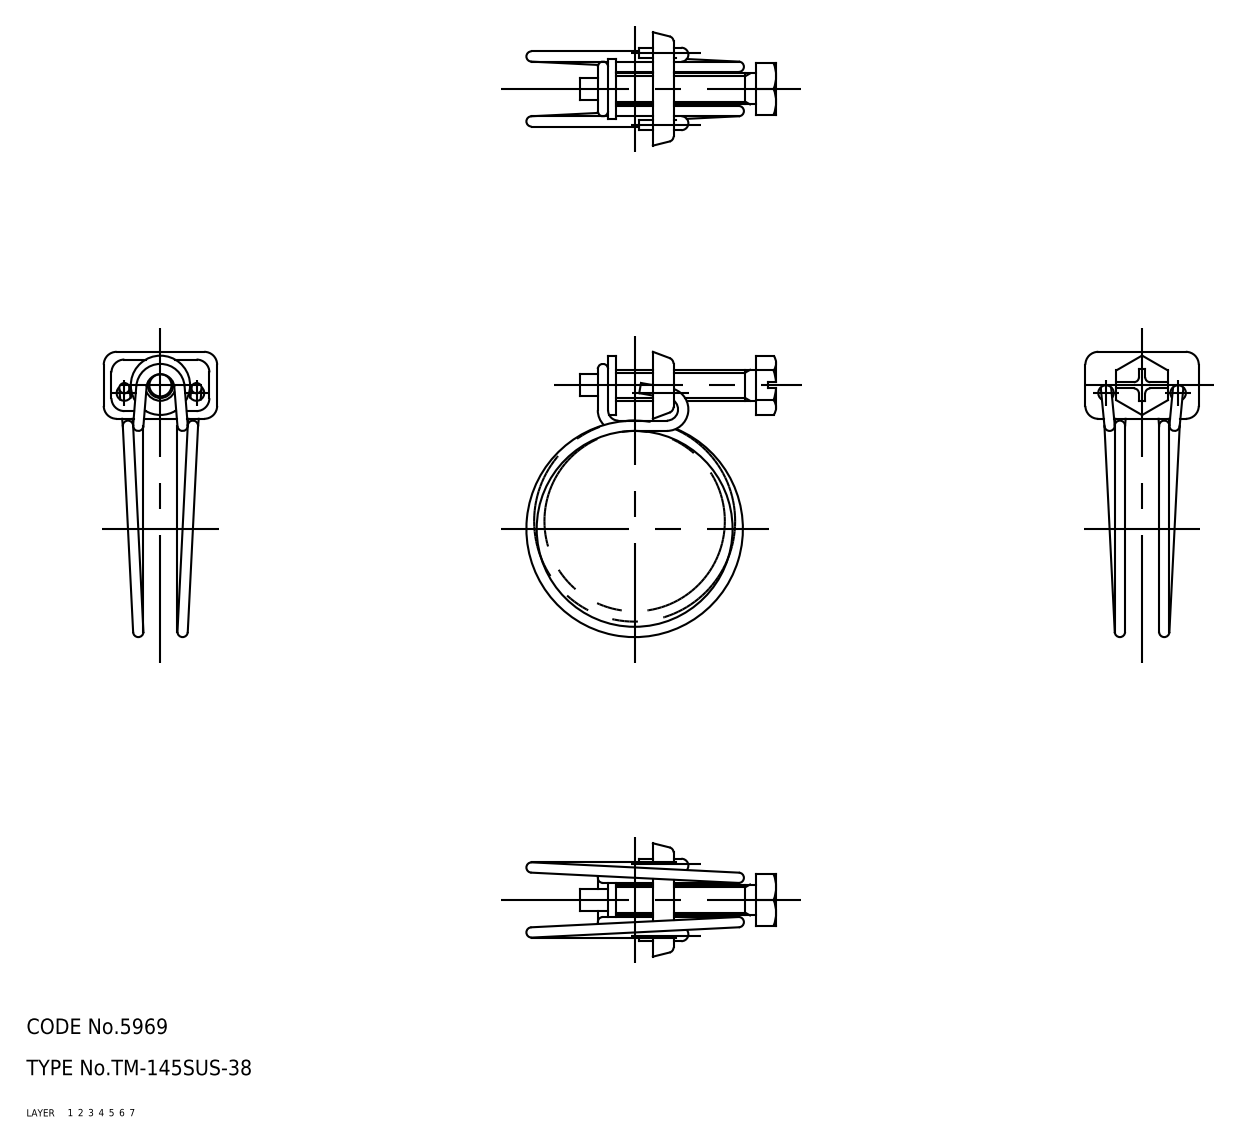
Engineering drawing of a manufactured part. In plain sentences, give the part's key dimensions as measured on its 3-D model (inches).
The part is named "screw; holder; band; TM_145SUS_38_22092_36". Its 3-D file was written by "CADfix (AUTOMOTIVE_DESIGN)". It is 3 solids with 119 faces: 0 planar, 0 cylindrical and 119 other. Overall it measures 2.179 by 1.907 by 0.866 inches. Its volume is 0.174 cubic inches and its surface area 6.247 square inches.
